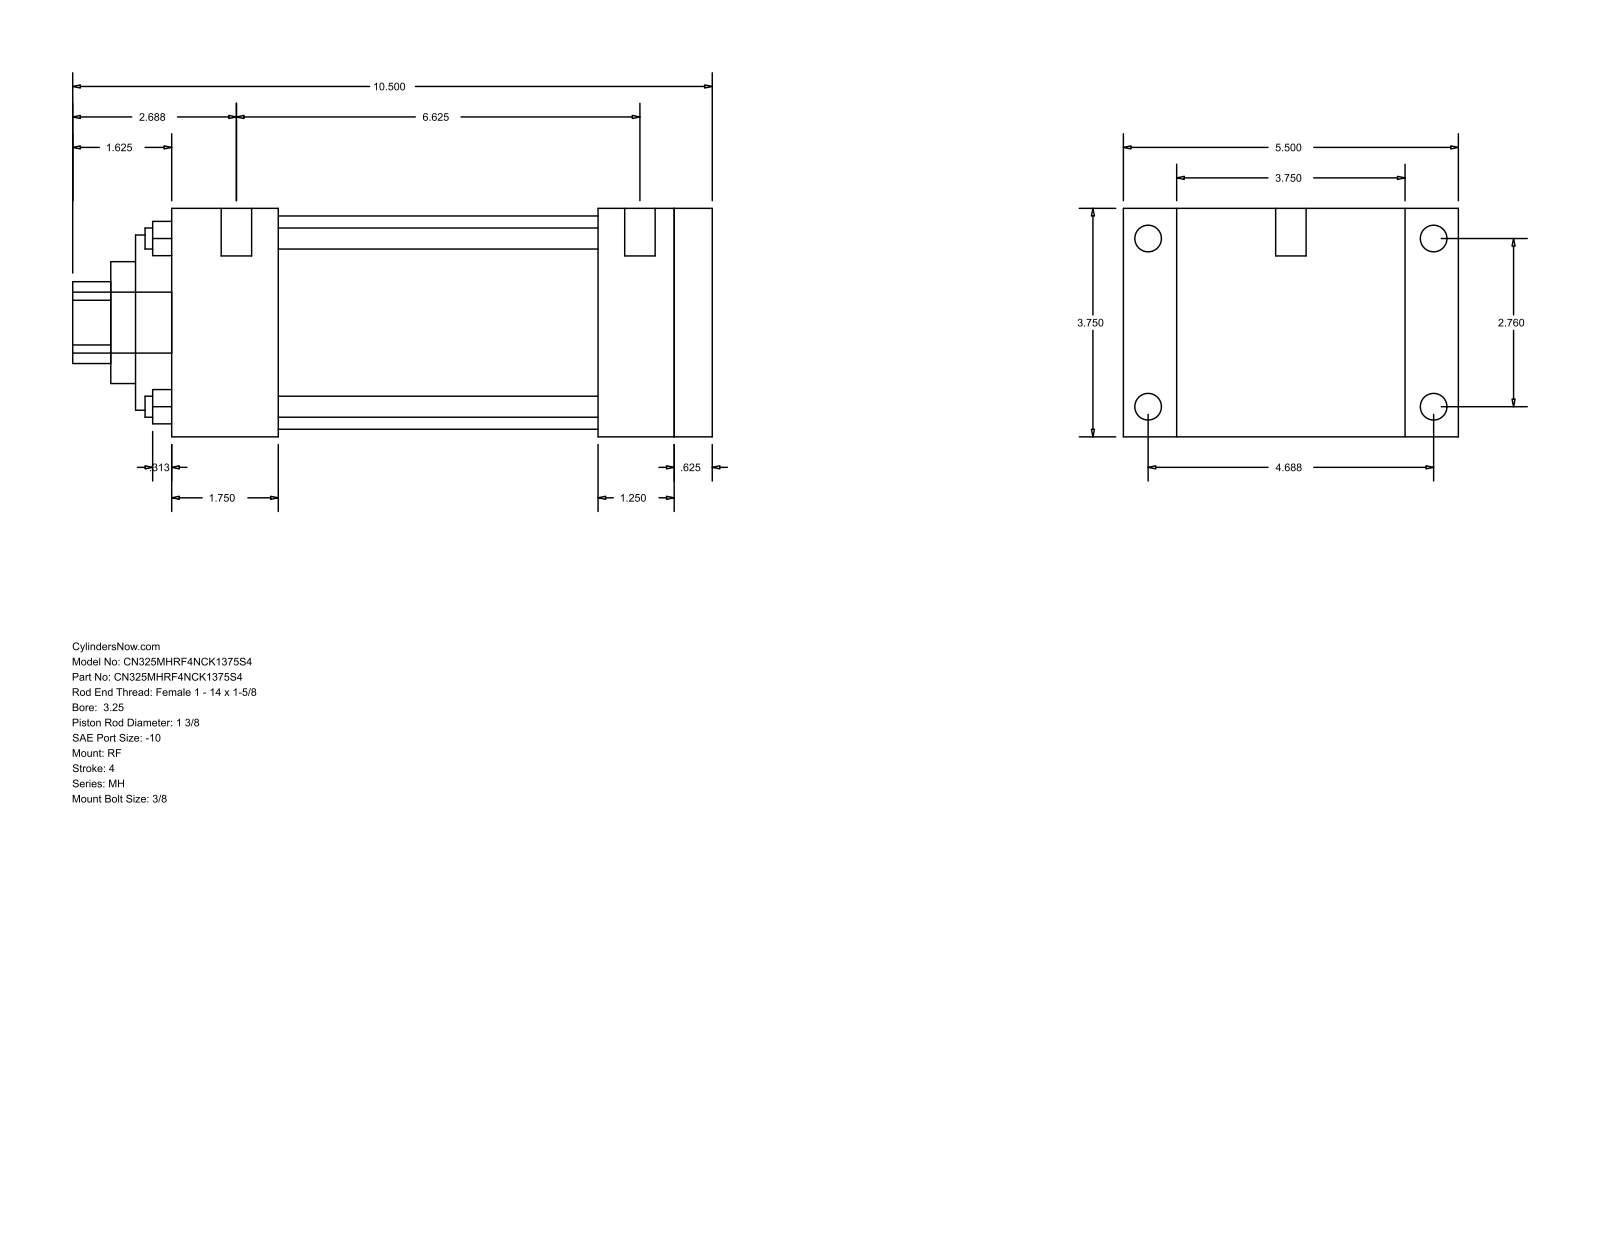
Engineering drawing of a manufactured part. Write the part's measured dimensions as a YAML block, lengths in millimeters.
part_name: "MH_RF__0325_1.375"
step_written_by: "GSSL Pune (CONFIG_CONTROL_DESIGN)"
units: millimeters
bodies: {solids: 0, faces: 94, planar: 65, cylindrical: 29, other: 0}
overall_size: [266.7, 139.7, 95.25]
round_holes:
  - {diameter: 8.76, count: 4}
  - {diameter: 34.92, count: 1}
  - {diameter: 50.8, count: 1}
  - {diameter: 73.03, count: 1}
  - {diameter: 88.9, count: 1}
round_bosses_or_shafts:
  - {diameter: 11.13, count: 4}
  - {diameter: 5.56, count: 4}
  - {diameter: 12.7, count: 2}
  - {diameter: 25.4, count: 1}
partial_cylinders:
  - {radius: 17.06, count: 1}
face_to_face_distances: [95.24, 225.43, 15.88, 209.55, 22.23, 117.47, 44.45, 165.1, 180.98, 177.8]
hole_center_spacings: [49.57, 70.1, 99.14]
